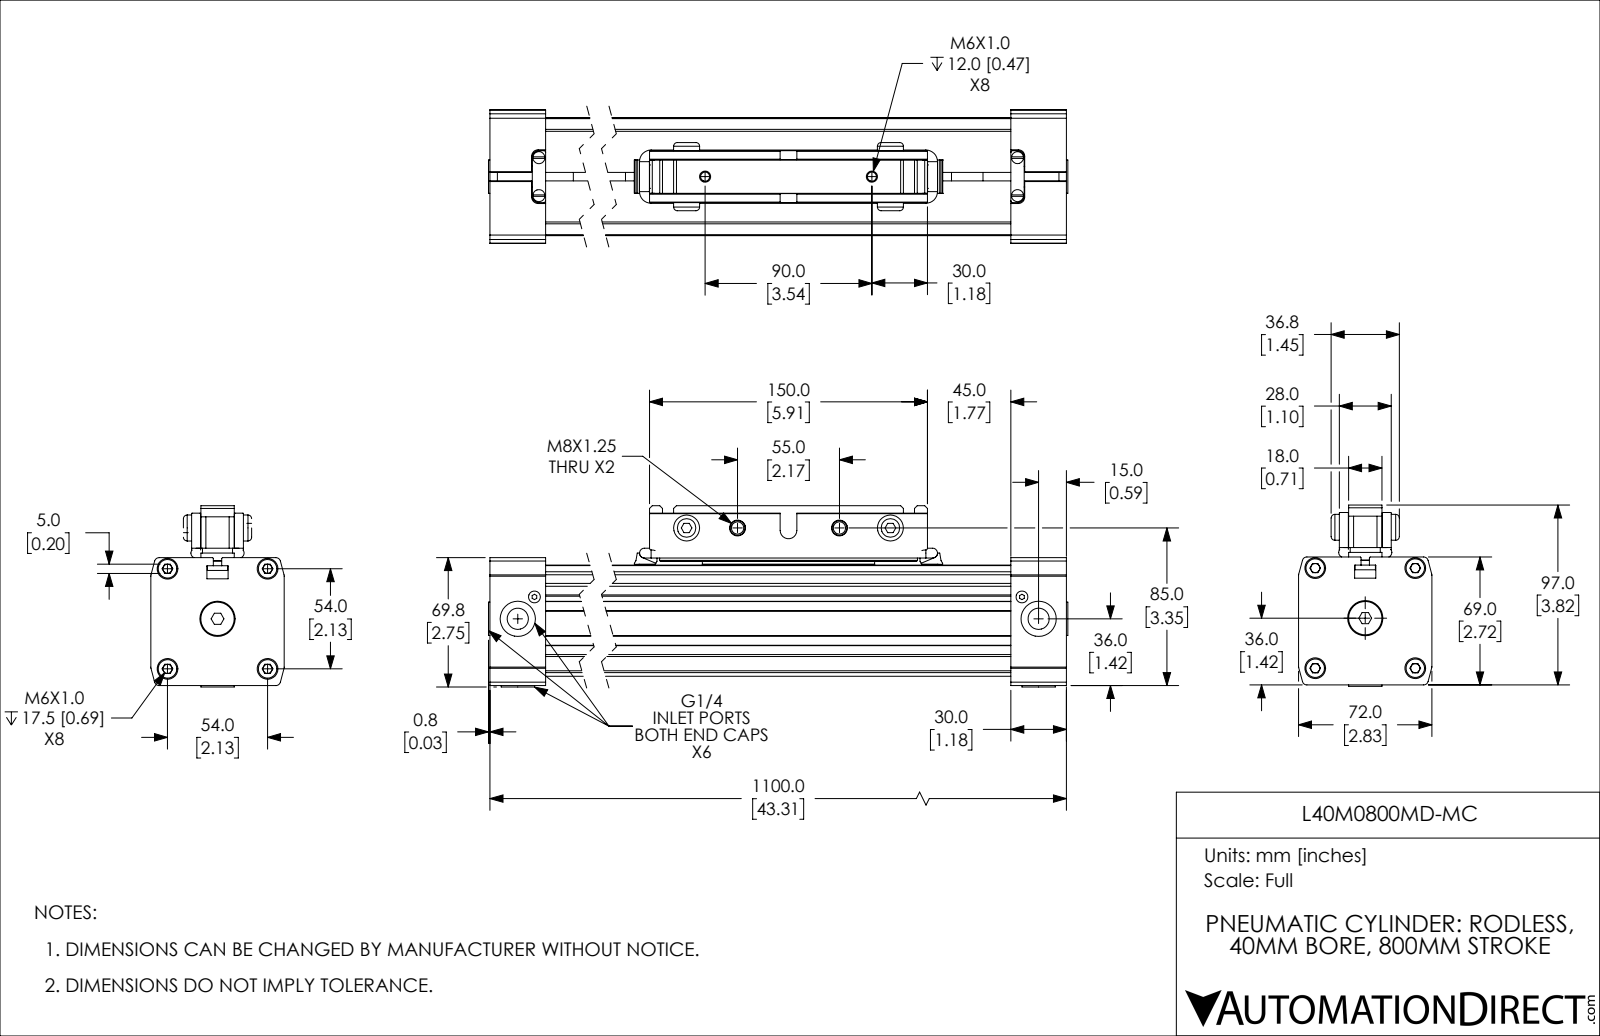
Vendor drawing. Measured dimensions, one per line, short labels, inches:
name: L40M0800MD-MC_BODY; L40M0800MD-MC_PISTON; L40M0800MD-MC
written by: SolidWorks 2019 (CONFIG_CONTROL_DESIGN)
unit: in
bodies: 13 solids, 821 faces (451 planar, 278 cylindrical, 92 other)
size: 43.369 × 3.85 × 2.835
volume: 173 in³; area: 926.4 in²
holes: 6× ⌀0.194, 5× ⌀0.748, 4× ⌀0.256, 4× ⌀0.262, 4× ⌀0.339, 4× ⌀0.441, 3× ⌀0.451, 2× ⌀0.252, 2× ⌀0.451, 1× ⌀1.583
bosses: 4× ⌀0.394, 4× ⌀0.21, 3× ⌀0.709, 3× ⌀0.437, 2× ⌀0.551, 2× ⌀0.518, 1× ⌀1.575, 1× ⌀0.518
rounds: 30× R0.039, 10× R0.079, 8× R0.012, 8× R0.098, 8× R0.138, 4× R0.157, 2× R0.006, 2× R0.008
face distances: 2.362, 0.201, 2.504, 2.303, 0.732, 0.274, 1.45, 0.031, 0.701, 1.161
hole spacings: 0.604, 1.503, 2.126, 41.679, 0.584, 0.807, 1.083, 1.428
